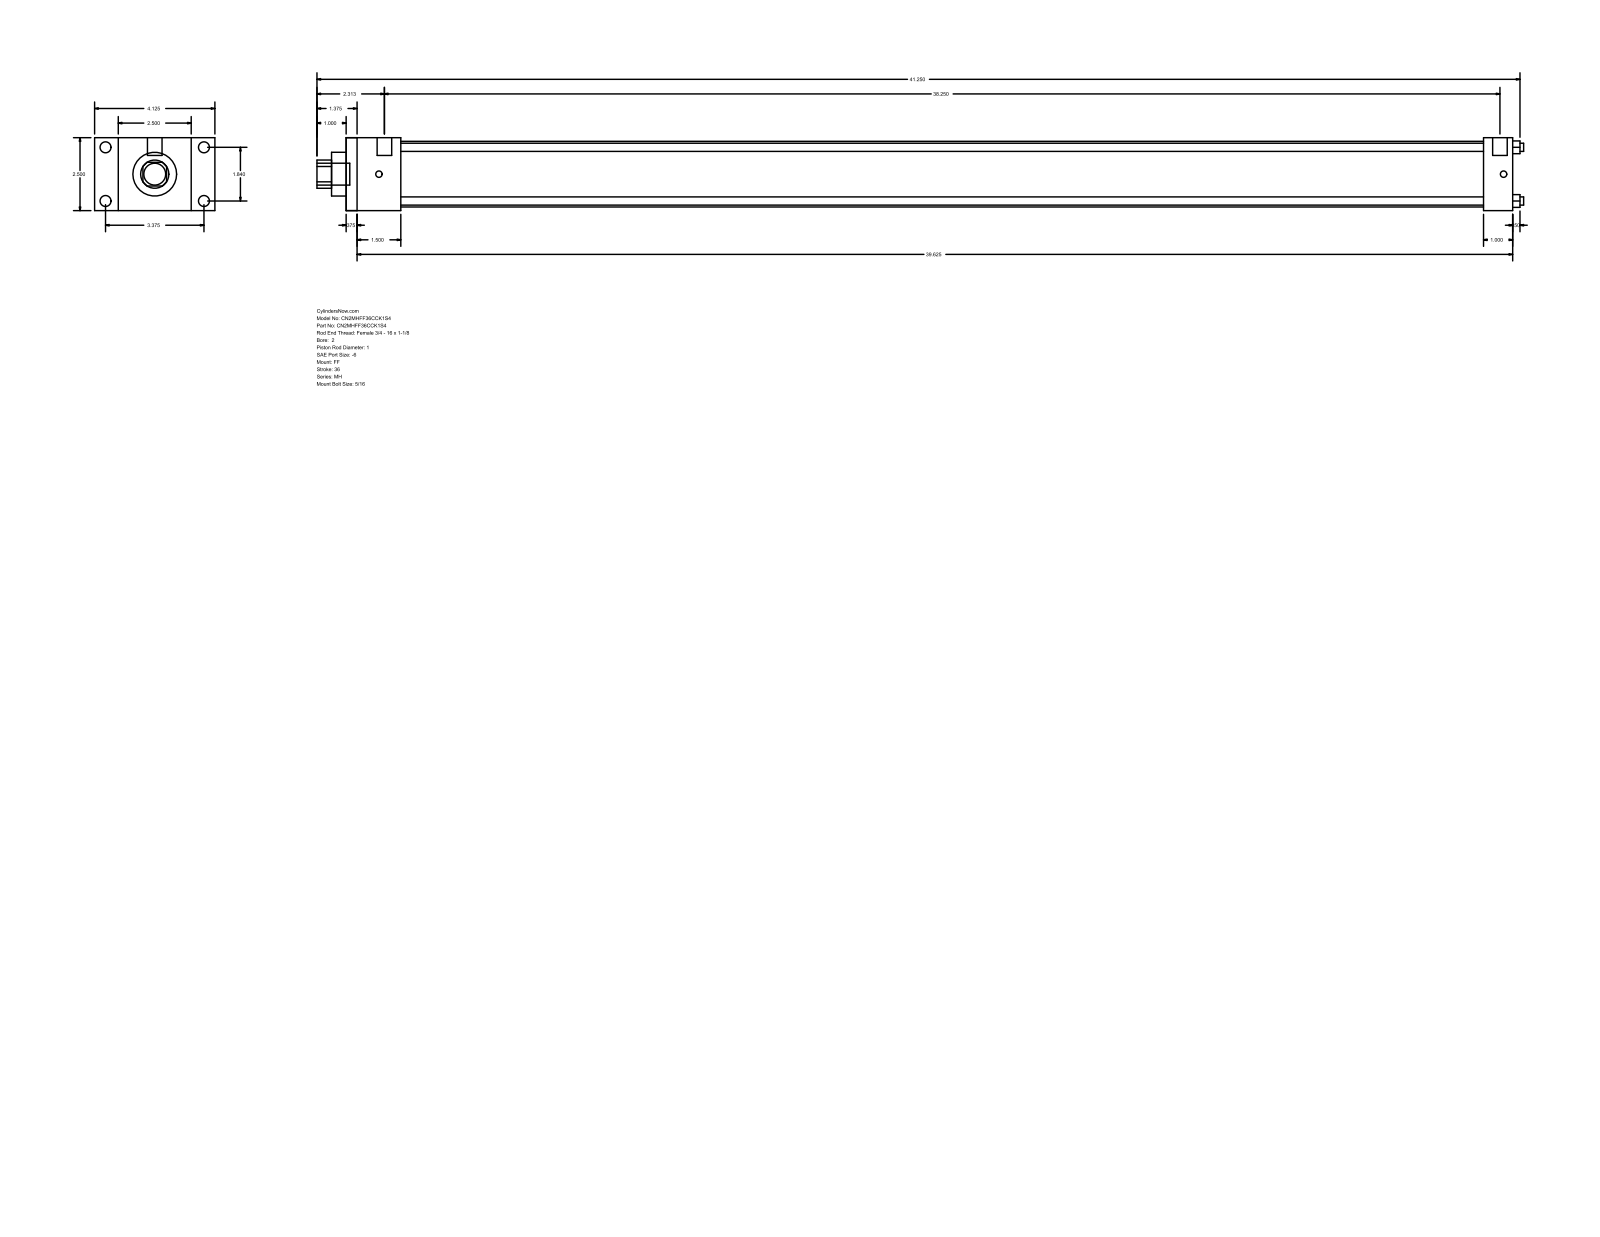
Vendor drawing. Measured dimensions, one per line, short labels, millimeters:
name: MH_FF__0200_1
written by: GSSL Pune (CONFIG_CONTROL_DESIGN)
unit: mm
bodies: 0 solids, 92 faces (64 planar, 28 cylindrical, 0 other)
size: 1050.92 × 104.78 × 63.5
holes: 4× ⌀7.14, 1× ⌀25.4, 1× ⌀38.1, 1× ⌀57.15
bosses: 4× ⌀9.53, 4× ⌀5.56, 2× ⌀12.7, 1× ⌀19.05
rounds: 1× R12.29
face distances: 63.5, 1016, 9.52, 1006.48, 20.64, 25.4, 47.63, 990.6, 38.11, 981.08
hole spacings: 33.05, 46.74, 66.1
